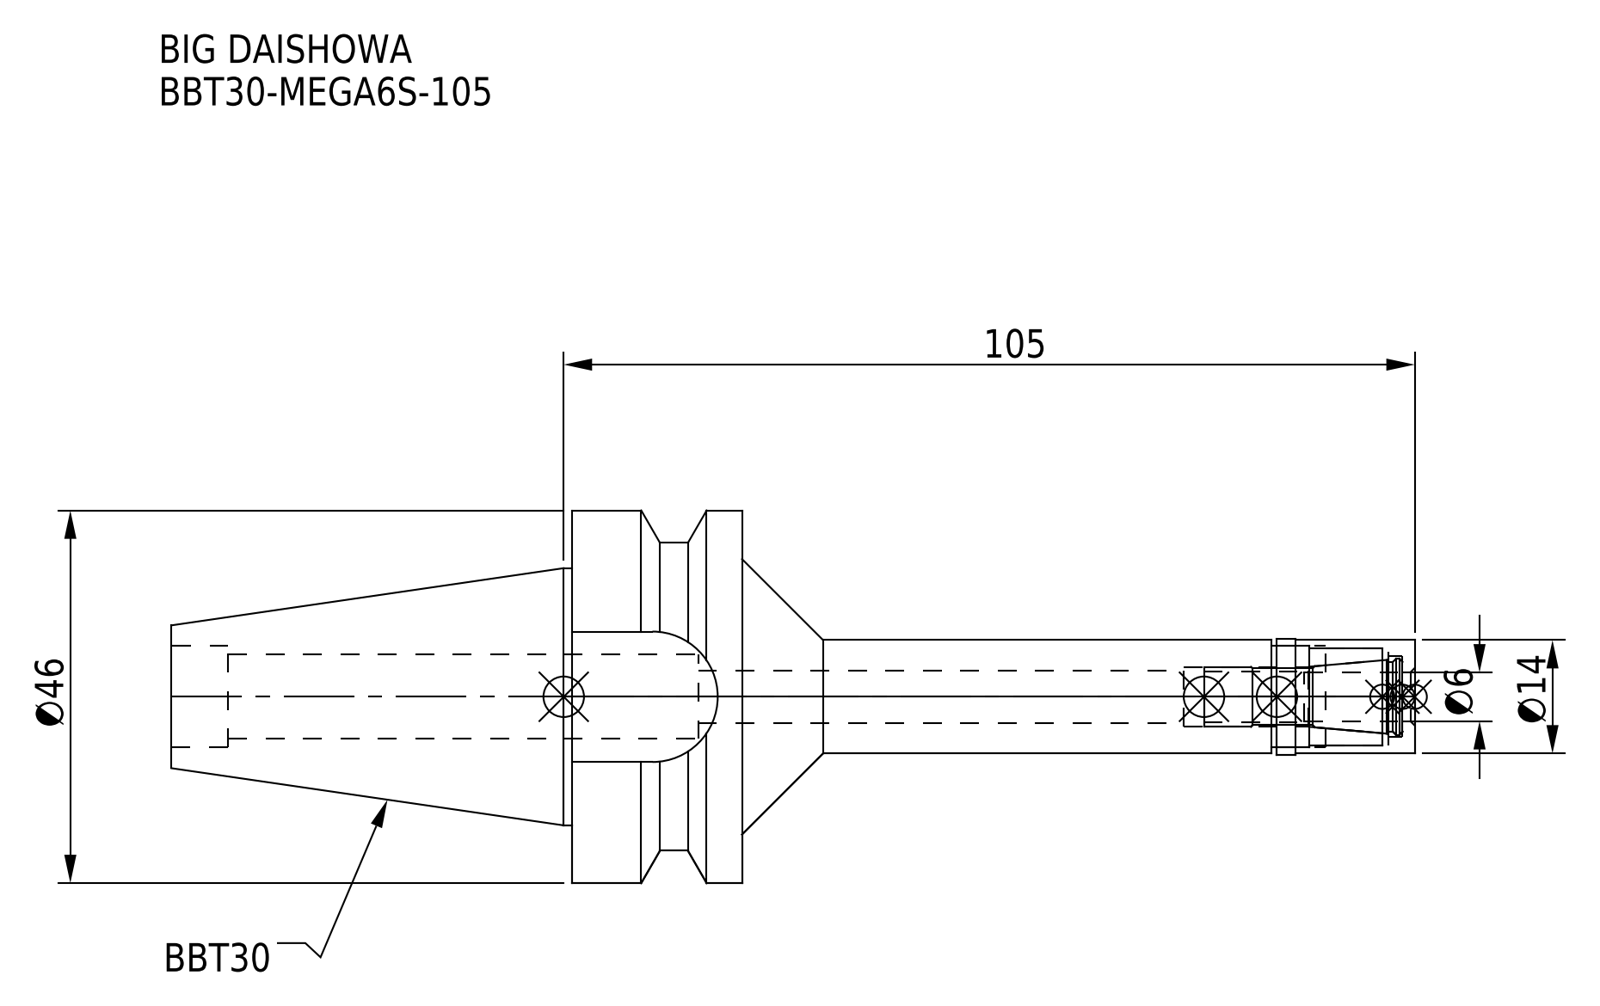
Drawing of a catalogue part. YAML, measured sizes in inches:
part_name: "BBT30-MEGA6S-105_1.stp; MGN6S_1.stp; DXF_TEMP_ASSY_ASM_4_ASM.stp; BBT30MS06105-060_ASM.stp (+3 more)"
step_written_by: "SolidWorks 2019 (CONFIG_CONTROL_DESIGN)"
units: inches
bodies: {solids: 2, faces: 71, planar: 21, cylindrical: 38, other: 12}
overall_size: [6.039, 1.811, 1.811]
volume: 3.705
surface_area: 29.45
round_holes:
  - {diameter: 0.24, count: 1}
  - {diameter: 0.252, count: 1}
  - {diameter: 0.291, count: 1}
  - {diameter: 0.394, count: 1}
  - {diameter: 0.409, count: 1}
  - {diameter: 0.472, count: 1}
  - {diameter: 0.492, count: 1}
round_bosses_or_shafts:
  - {diameter: 1.811, count: 1}
  - {diameter: 1.25, count: 1}
  - {diameter: 0.563, count: 1}
  - {diameter: 0.551, count: 1}
  - {diameter: 0.551, count: 1}
  - {diameter: 0.492, count: 1}
  - {diameter: 0.472, count: 1}
partial_cylinders:
  - {radius: 0.317, count: 1}
  - {radius: 0.748, count: 1}
face_to_face_distances: [0.827, 1.283, 2.772, 1.945, 3.268, 4.094, 6.039, 0.634, 0.028, 0.539]
